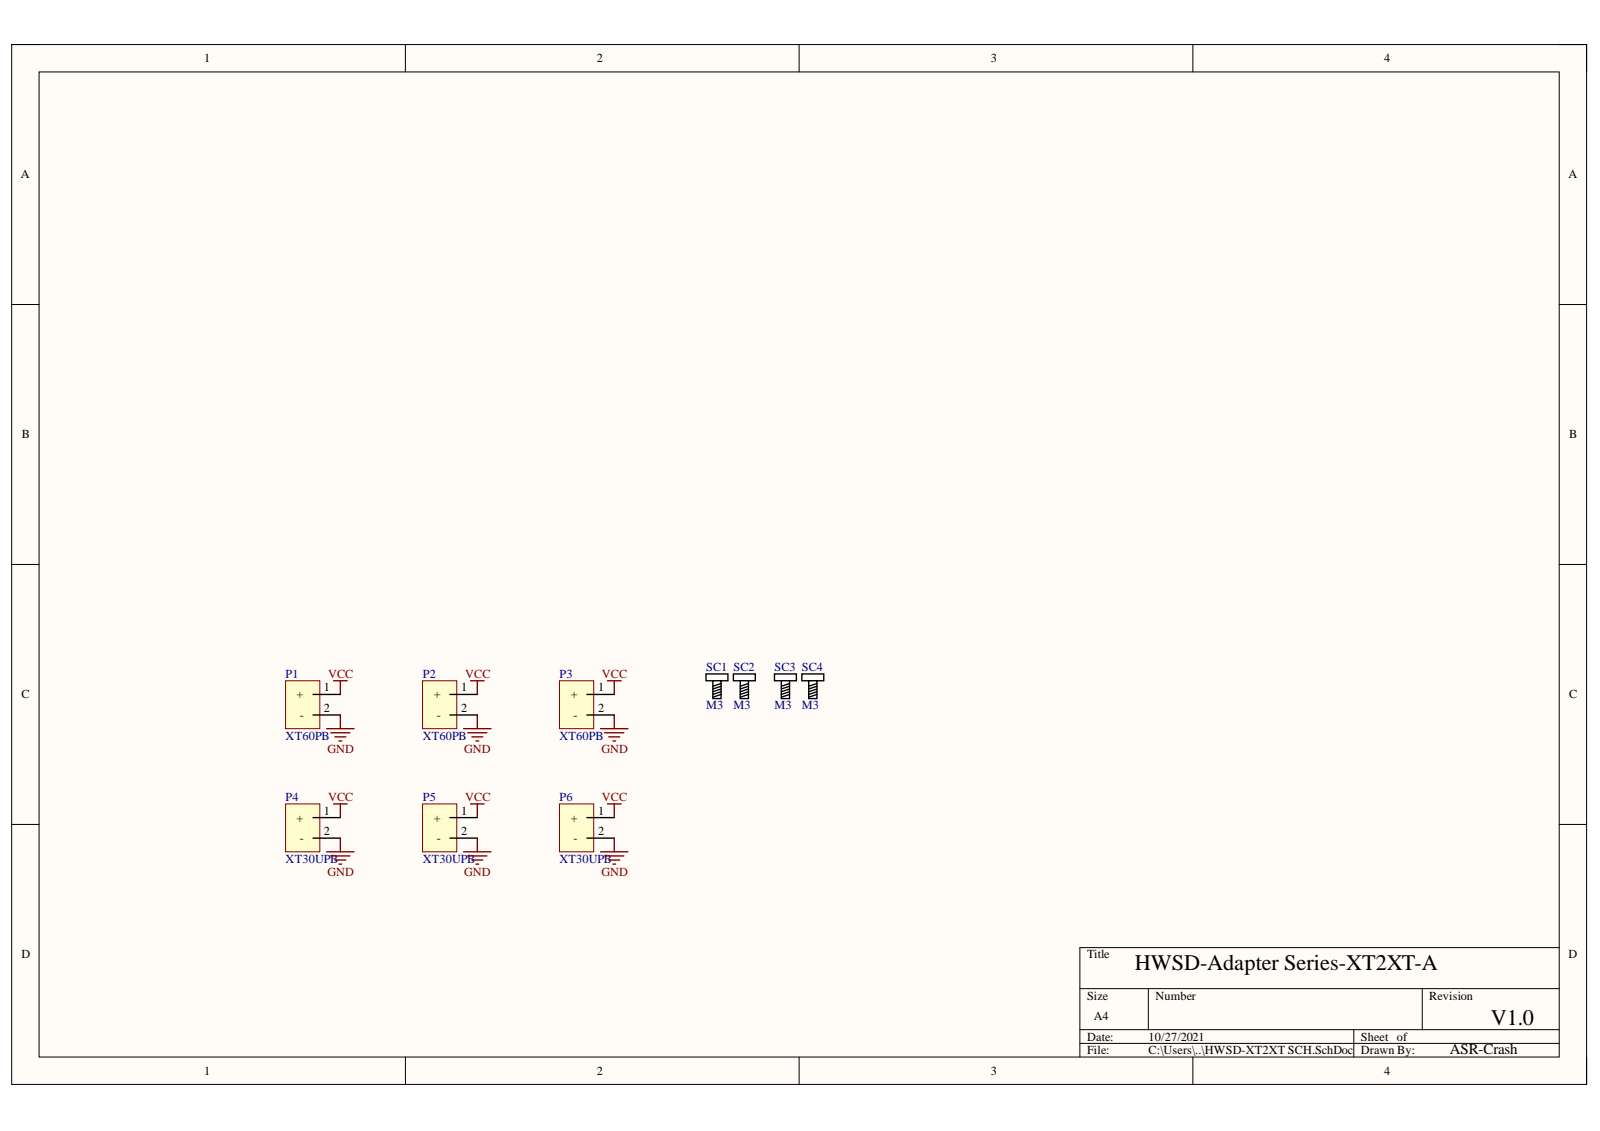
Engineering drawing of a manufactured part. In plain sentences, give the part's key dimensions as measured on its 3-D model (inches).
The part is named "PCB; Board; P6; XT30UPB-M (+7 more)". Its 3-D file was written by "Open CASCADE 6.8 (AUTOMOTIVE_DESIGN)". It is 11 solids with 1985 faces: 1075 planar, 510 cylindrical and 400 other. Overall it measures 1.974 by 1.186 by 0.801 inches. Its volume is 0.401 cubic inches and its surface area 15.49 square inches. Round holes: 6 of diameter 0.071, 6 of diameter 0.177, 4 of diameter 0.087, 4 of diameter 0.102, 4 of diameter 0.118, 4 of diameter 0.138, 2 of diameter 0.098, 2 of diameter 0.126, 2 of diameter 0.157, 2 of diameter 0.197. Round bosses or shafts: 6 of diameter 0.063, 4 of diameter 0.165. Partial cylindrical surfaces (rounded edges, fillets, slot ends): 78 of radius 0.004, 58 of radius 0.01, 28 of radius 0.012, 18 of radius 0.02, 14 of radius 0.008, 14 of radius 0.039, 6 of radius 0.059, 6 of radius 0.071. The main face-to-face distances are 0.067, 0.02, 0.027, 0.264, 0.736, 0.039, 0.024, 0.387, 0.087, 0.293. The hole center spacings are 0.197, 0.736, 0.981, 0.368, 0.368, 0.501, 0.629, 0.698.
